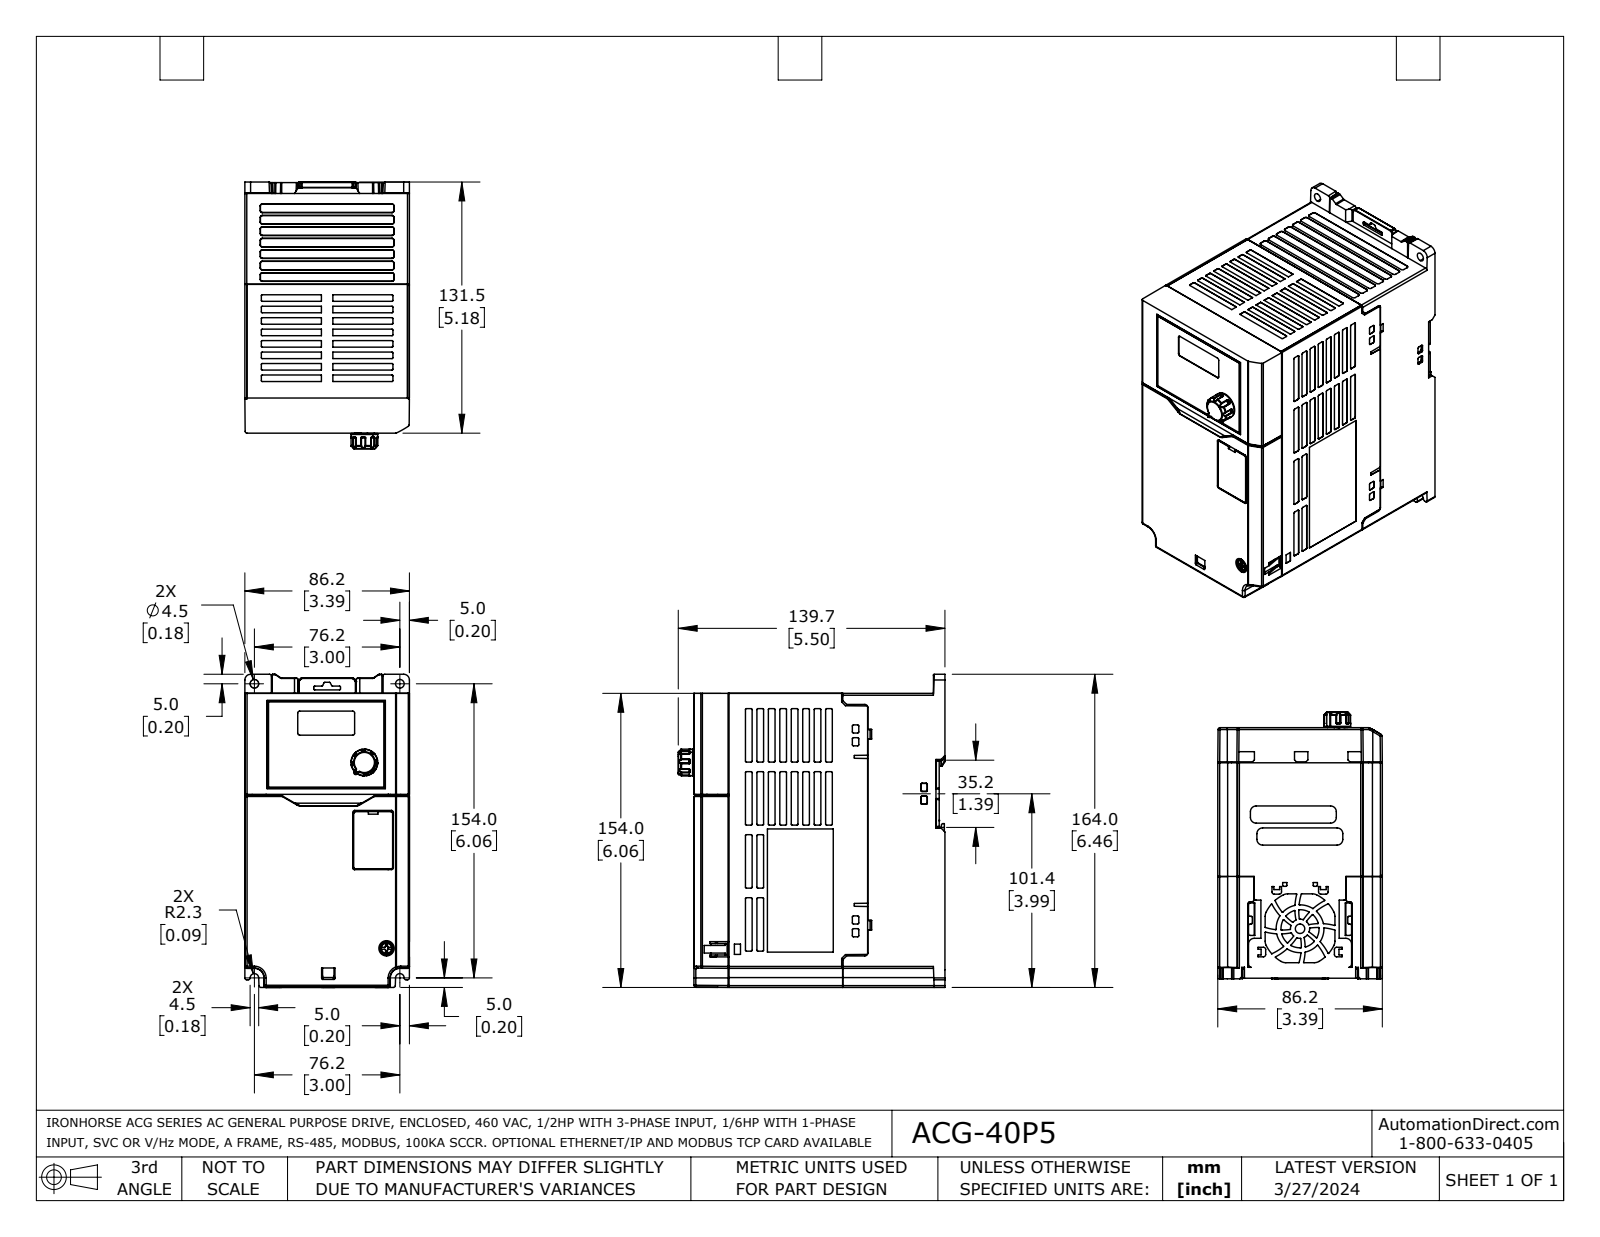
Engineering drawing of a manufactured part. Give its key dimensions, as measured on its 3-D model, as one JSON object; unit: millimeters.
{"part_name": "ACG-40P5", "step_written_by": "SolidWorks 2021 (AUTOMOTIVE_DESIGN)", "units": "millimeters", "bodies": {"solids": 6, "faces": 4492, "planar": 1868, "cylindrical": 1308, "other": 1316}, "overall_size": [164, 139.7, 86.2], "volume_mm3": 1670000, "surface_area_mm2": 127400, "round_holes": [[1, 1], [7, 1], [12, 1]], "round_bosses_or_shafts": [[14, 1], [13.8, 1], [6, 1]], "partial_cylinders_radius": [[0.2, 343], [0.5, 288], [1, 85], [0.5, 46], [0.3, 27], [0.8, 17], [0.6, 16], [3, 12]], "face_to_face_distances": [86.2, 128.5, 86.2, 128.2, 154, 153.9, 131.2, 2.7, 86.1, 153.9], "hole_center_spacings": [7, 93.3, 98]}
